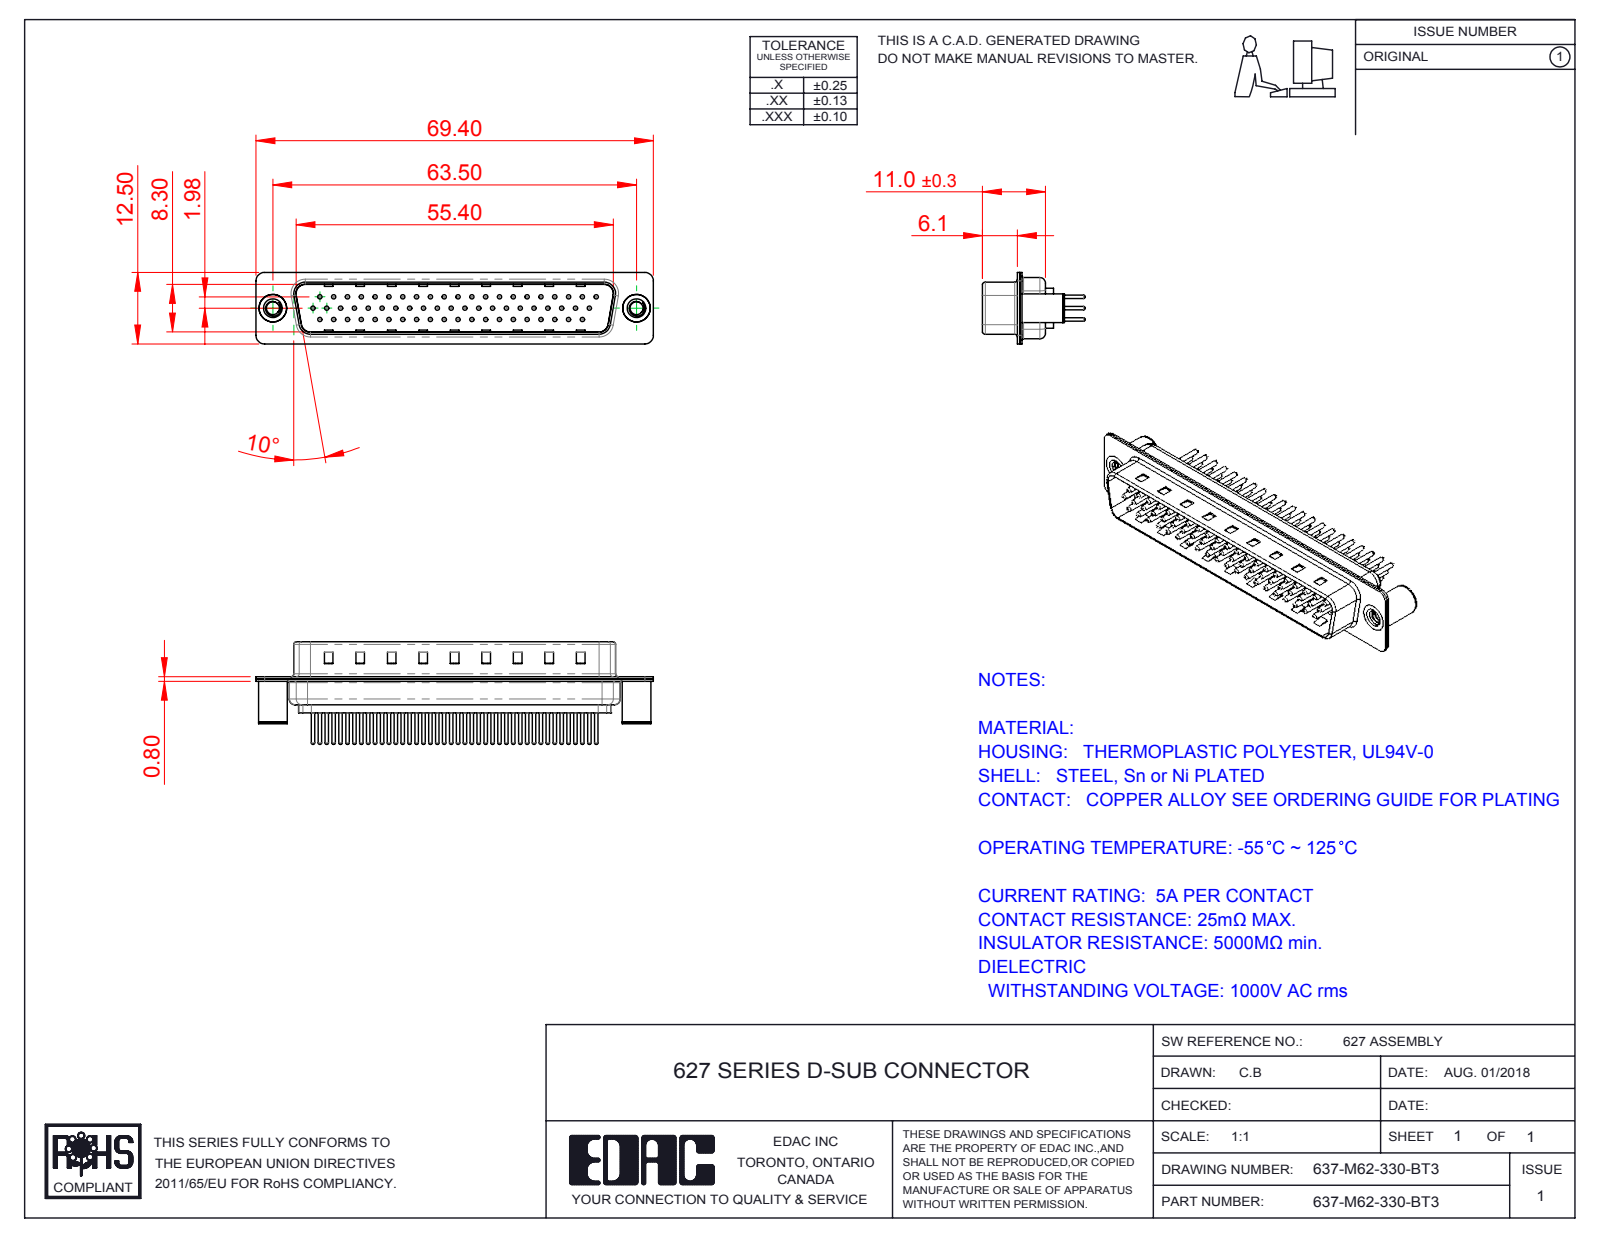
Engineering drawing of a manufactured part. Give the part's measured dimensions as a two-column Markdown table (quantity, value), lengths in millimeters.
| quantity | value |
| --- | --- |
| part name | 637M 4-40 Threaded Board Spacer; 637-M62-330-BT3; 637M Contact Row 2_30; 637M Housing_62 Contacts (+4 more) |
| STEP written by | SolidWorks 2016 (CONFIG_CONTROL_DESIGN) |
| units | millimeters |
| bodies | 67 solids, 2740 faces (637 planar, 1033 cylindrical, 1070 other) |
| overall size | 69.4 × 17.9 × 12.5 |
| volume | 4 040 mm³ |
| surface area | 11 672 mm² |
| round holes (diameter × count) | 0.75 × 62, 1.6 × 62, 2 × 62, 2.26 × 2, 3.26 × 2, 4 × 2, 4.8 × 2 |
| round bosses / shafts (diameter × count) | 1.5 × 62, 0.6 × 62, 5 × 2, 4.9 × 2 |
| partial cylindrical surfaces (radius × count) | 1.5 × 16, 2 × 12, 0.5 × 8, 1.6 × 8, 0.25 × 4, 0.6 × 4, 0.65 × 4, 0.9 × 4 |
| main face-to-face distances | 0.4, 0.8, 9.5, 9.1, 8.7, 9.9, 0.75, 0.35, 5.9, 1.2 |
| hole center spacings | 7.24, 2.32, 2.41, 4.13, 9.65, 4.83, 14.48, 11.04 |
